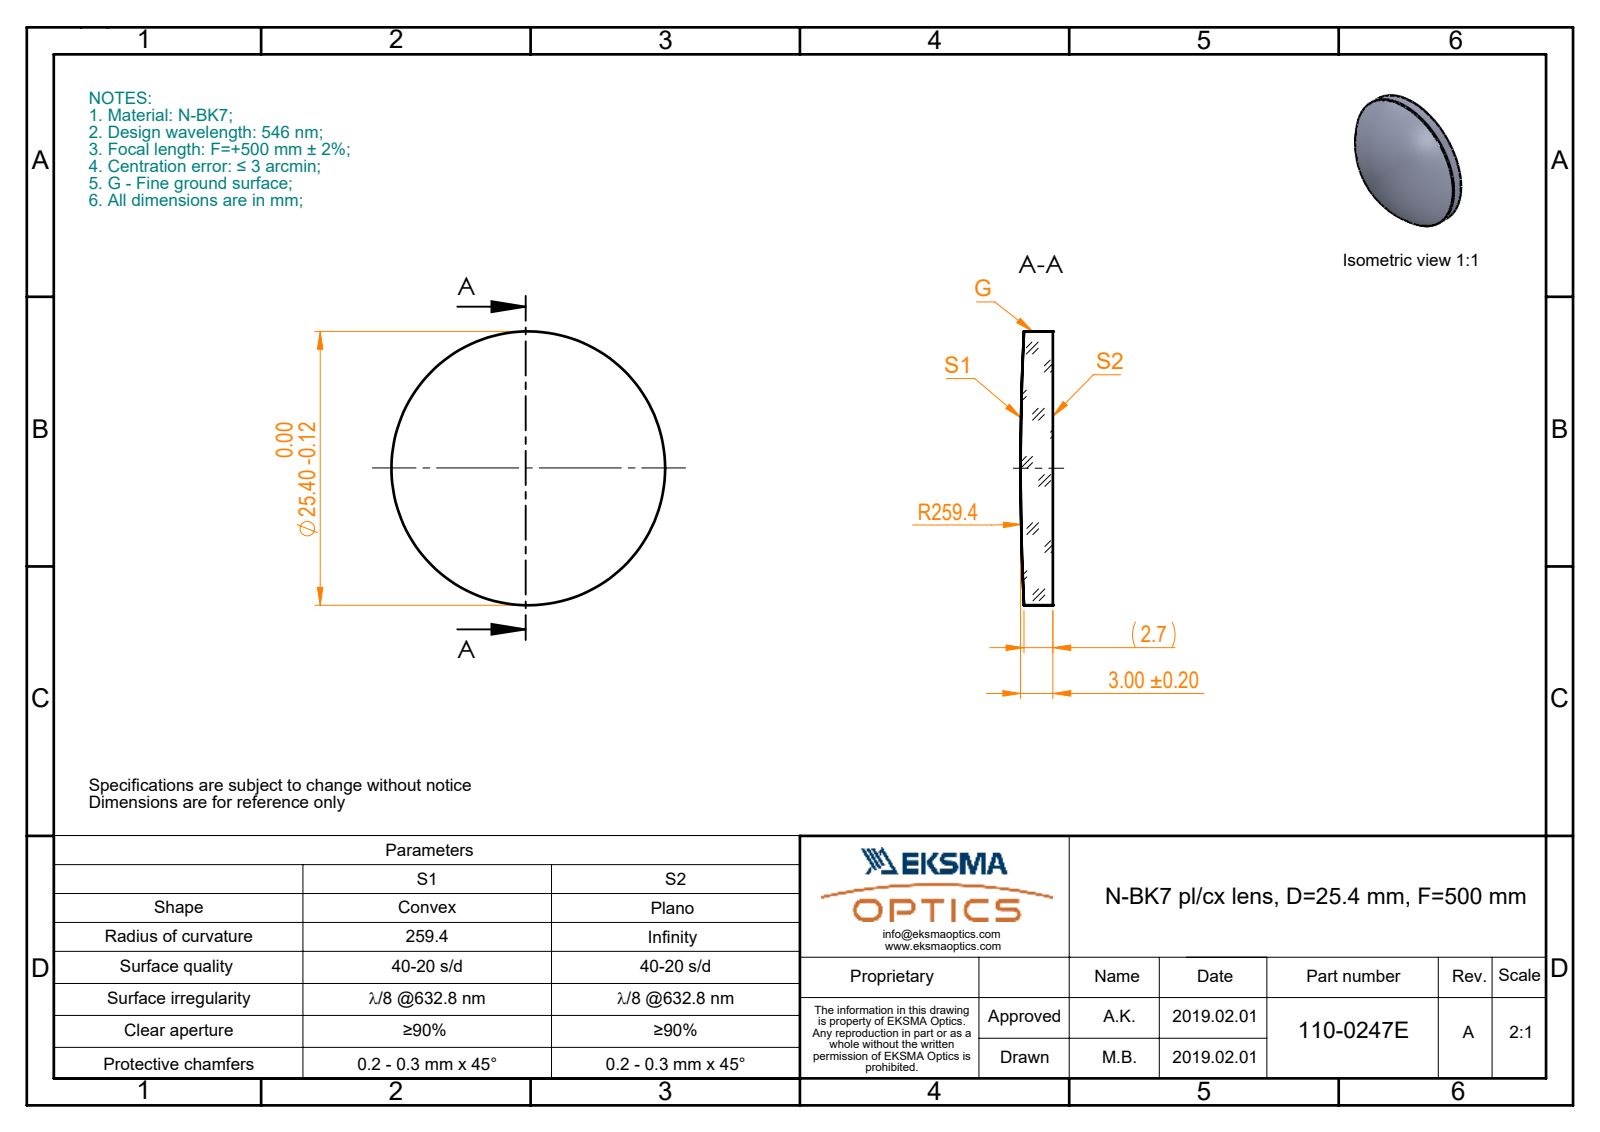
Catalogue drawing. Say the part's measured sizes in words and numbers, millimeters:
The part is named "110-0247E BK7 pl-cx 25.4 F500". Its 3-D file was written by "SolidWorks 2017 (CONFIG_CONTROL_DESIGN)". It is 1 solid with 5 faces: 1 planar, 2 cylindrical and 2 other. Overall it measures 25.4 by 25.4 by 3 millimeters. Its volume is 1 441 cubic millimeters and its surface area 1 228 square millimeters. Round bosses or shafts: 1 of diameter 25.4.
